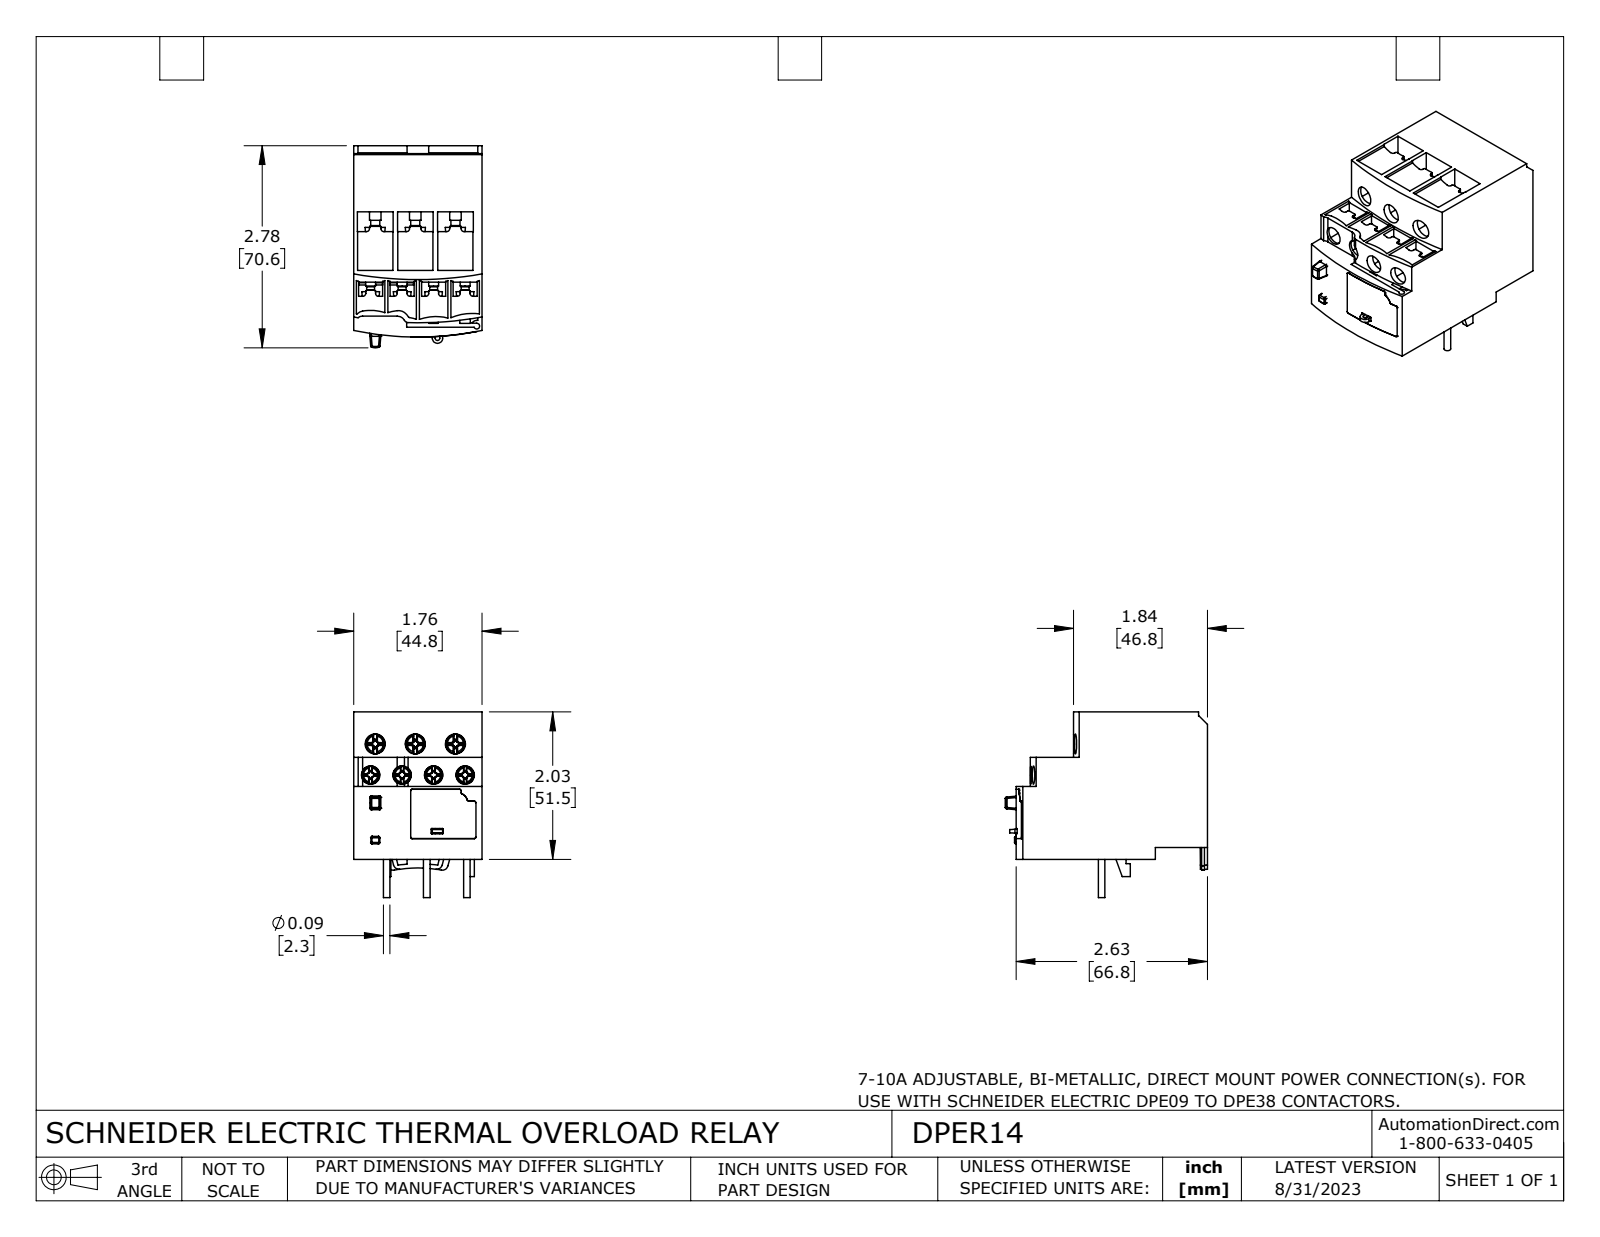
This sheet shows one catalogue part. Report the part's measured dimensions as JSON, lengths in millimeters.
{"part_name": "DPER14", "step_written_by": "SolidWorks 2021 (CONFIG_CONTROL_DESIGN)", "units": "millimeters", "bodies": {"solids": 16, "faces": 1212, "planar": 676, "cylindrical": 269, "other": 267}, "overall_size": [70.6, 64.8, 44.8], "volume_mm3": 113900, "surface_area_mm2": 30420, "round_holes": [[6.4, 4], [7, 3], [2, 2], [3, 2], [1.5, 1], [6.2, 1]], "round_bosses_or_shafts": [[2.3, 12], [3.5, 4], [2.7, 4], [4, 3], [3.9, 3], [3.1, 3], [3, 1], [2.7, 1]], "partial_cylinders_radius": [[0.5, 52], [1, 22], [0.1, 19], [0.3, 8], [0.2, 6], [16, 6], [2, 4], [0.6, 2]], "face_to_face_distances": [44.8, 4.2, 51.5, 47.3, 23.1, 14, 15.7, 35.8, 31.6, 63.4], "hole_center_spacings": [11, 14, 22, 8.5, 9.7, 10.3, 10.7, 11.4]}
